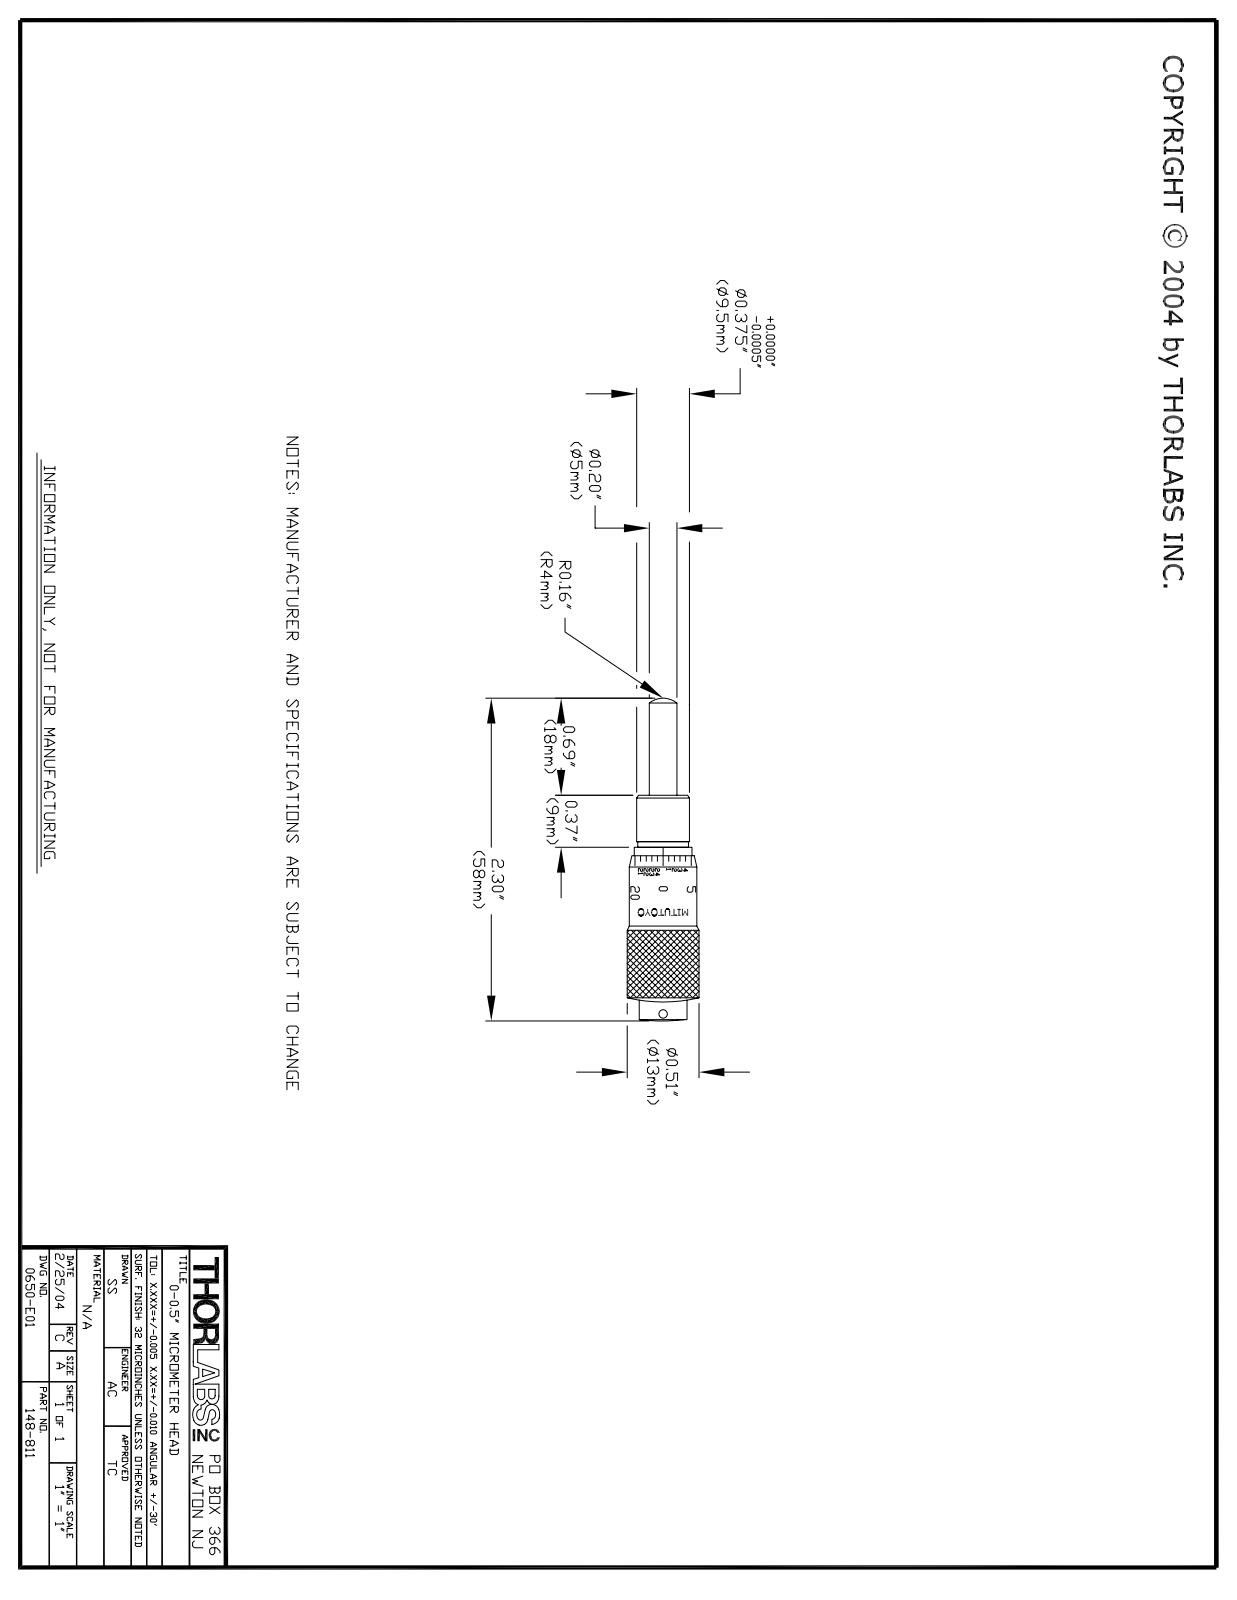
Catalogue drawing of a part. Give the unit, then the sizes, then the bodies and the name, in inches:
Units: inches
Overall size (bounding box): 2.295 × 0.51 × 0.51
Round holes (diameter × count): ⌀0.06 ×1
Round bosses / shafts (diameter × count): ⌀0.51 ×1, ⌀0.48 ×1, ⌀0.41 ×1, ⌀0.375 ×1, ⌀0.36 ×1, ⌀0.34 ×1, ⌀0.197 ×1
Main face-to-face distances: 0.37, 0.43, 0.06, 0.33, 0.04, 0.1
Bodies: 0 solids, 32 faces (4 planar, 16 cylindrical, 12 other)
Part name (STEP PRODUCT): 0650-E0W
STEP written by: SolidWorks 2007 (AUTOMOTIVE_DESIGN)
